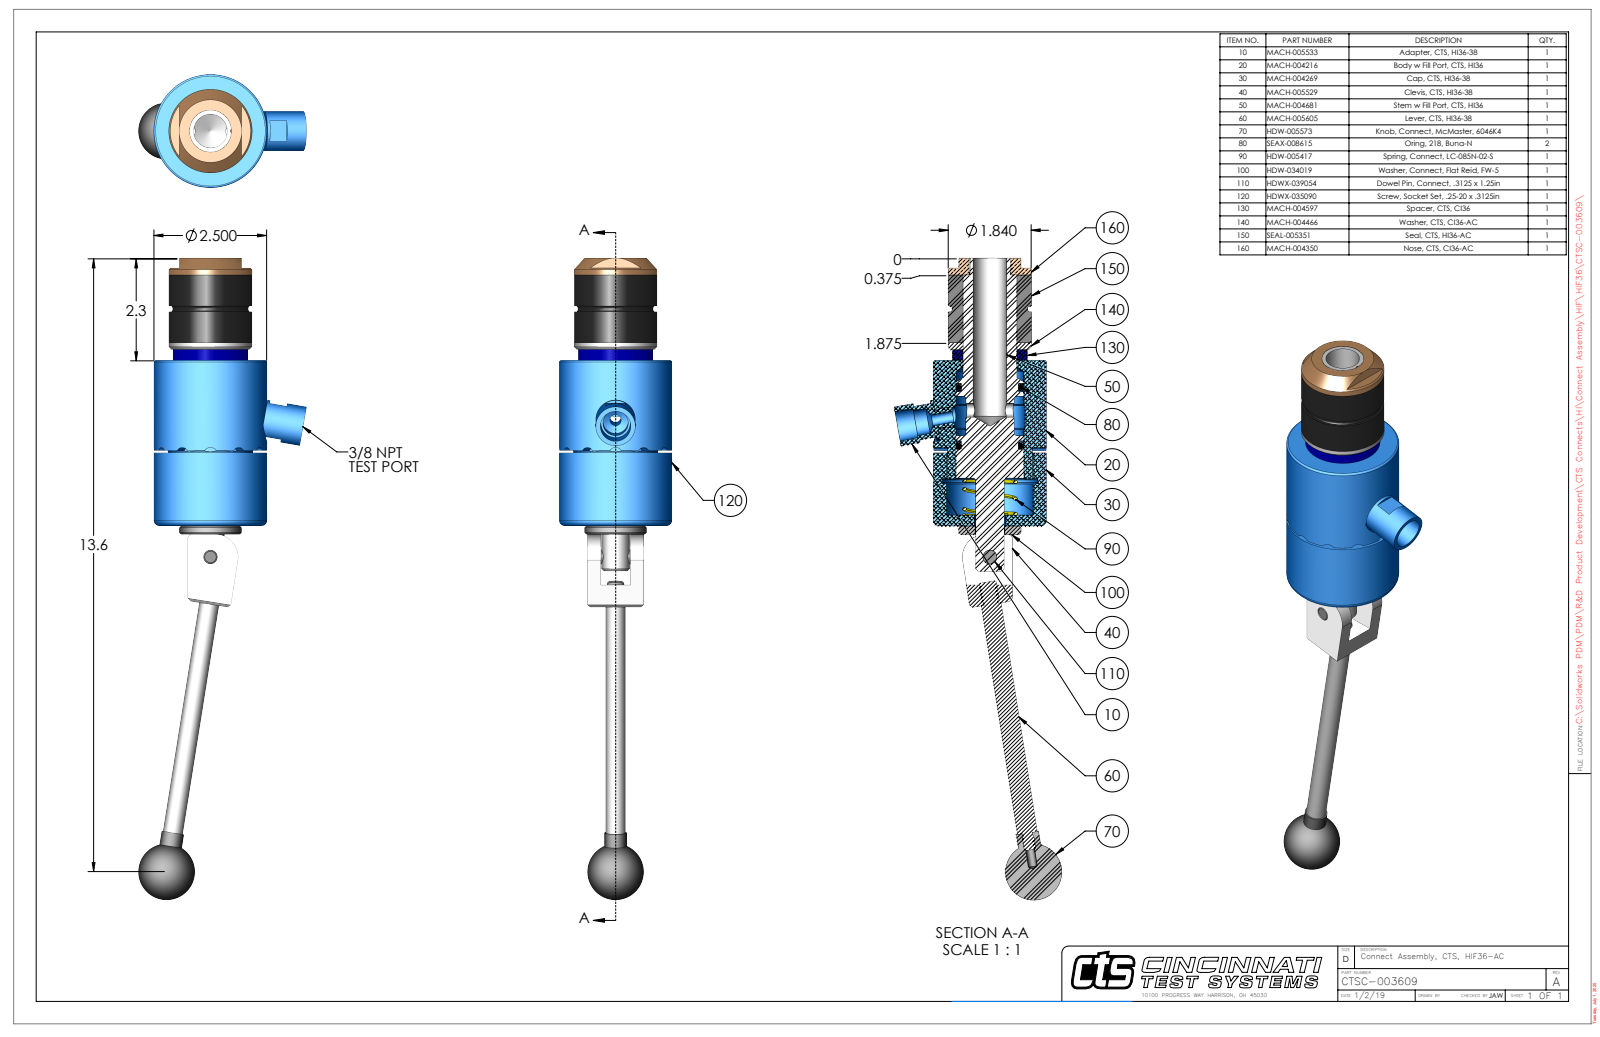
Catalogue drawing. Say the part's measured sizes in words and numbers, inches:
The part is named "CTSC-003609". Its 3-D file was written by "SolidWorks 2023 (AUTOMOTIVE_DESIGN)". It is 10 solids with 307 faces: 109 planar, 127 cylindrical and 71 other. Overall it measures 14.215 by 3.716 by 2.5 inches. Its volume is 25.73 cubic inches and its surface area 129.9 square inches. Round holes: 2 of diameter 0.201, 1 of diameter 0.15, 1 of diameter 0.25, 1 of diameter 0.311, 1 of diameter 0.312, 1 of diameter 0.313, 1 of diameter 0.314, 1 of diameter 0.562, 1 of diameter 0.656, 1 of diameter 0.696, 1 of diameter 0.75, 1 of diameter 0.922. Round bosses or shafts: 1 of diameter 2.5, 1 of diameter 1.875, 1 of diameter 1.84, 1 of diameter 1.656, 1 of diameter 1.38, 1 of diameter 1.186, 1 of diameter 1, 1 of diameter 0.904. Partial cylindrical surfaces (rounded edges, fillets, slot ends): 12 of radius 0.12, 2 of radius 0.029, 1 of radius 0.19, 1 of radius 0.195, 1 of radius 0.442, 1 of radius 0.47, 1 of radius 0.5, 1 of radius 1.176. The main face-to-face distances are 3.668, 5.555, 1.887, 4.055, 0.387, 1.5, 3.905, 0.237, 0.15, 1.65. The hole center spacings are 0.74, 2.118, 2.858.
